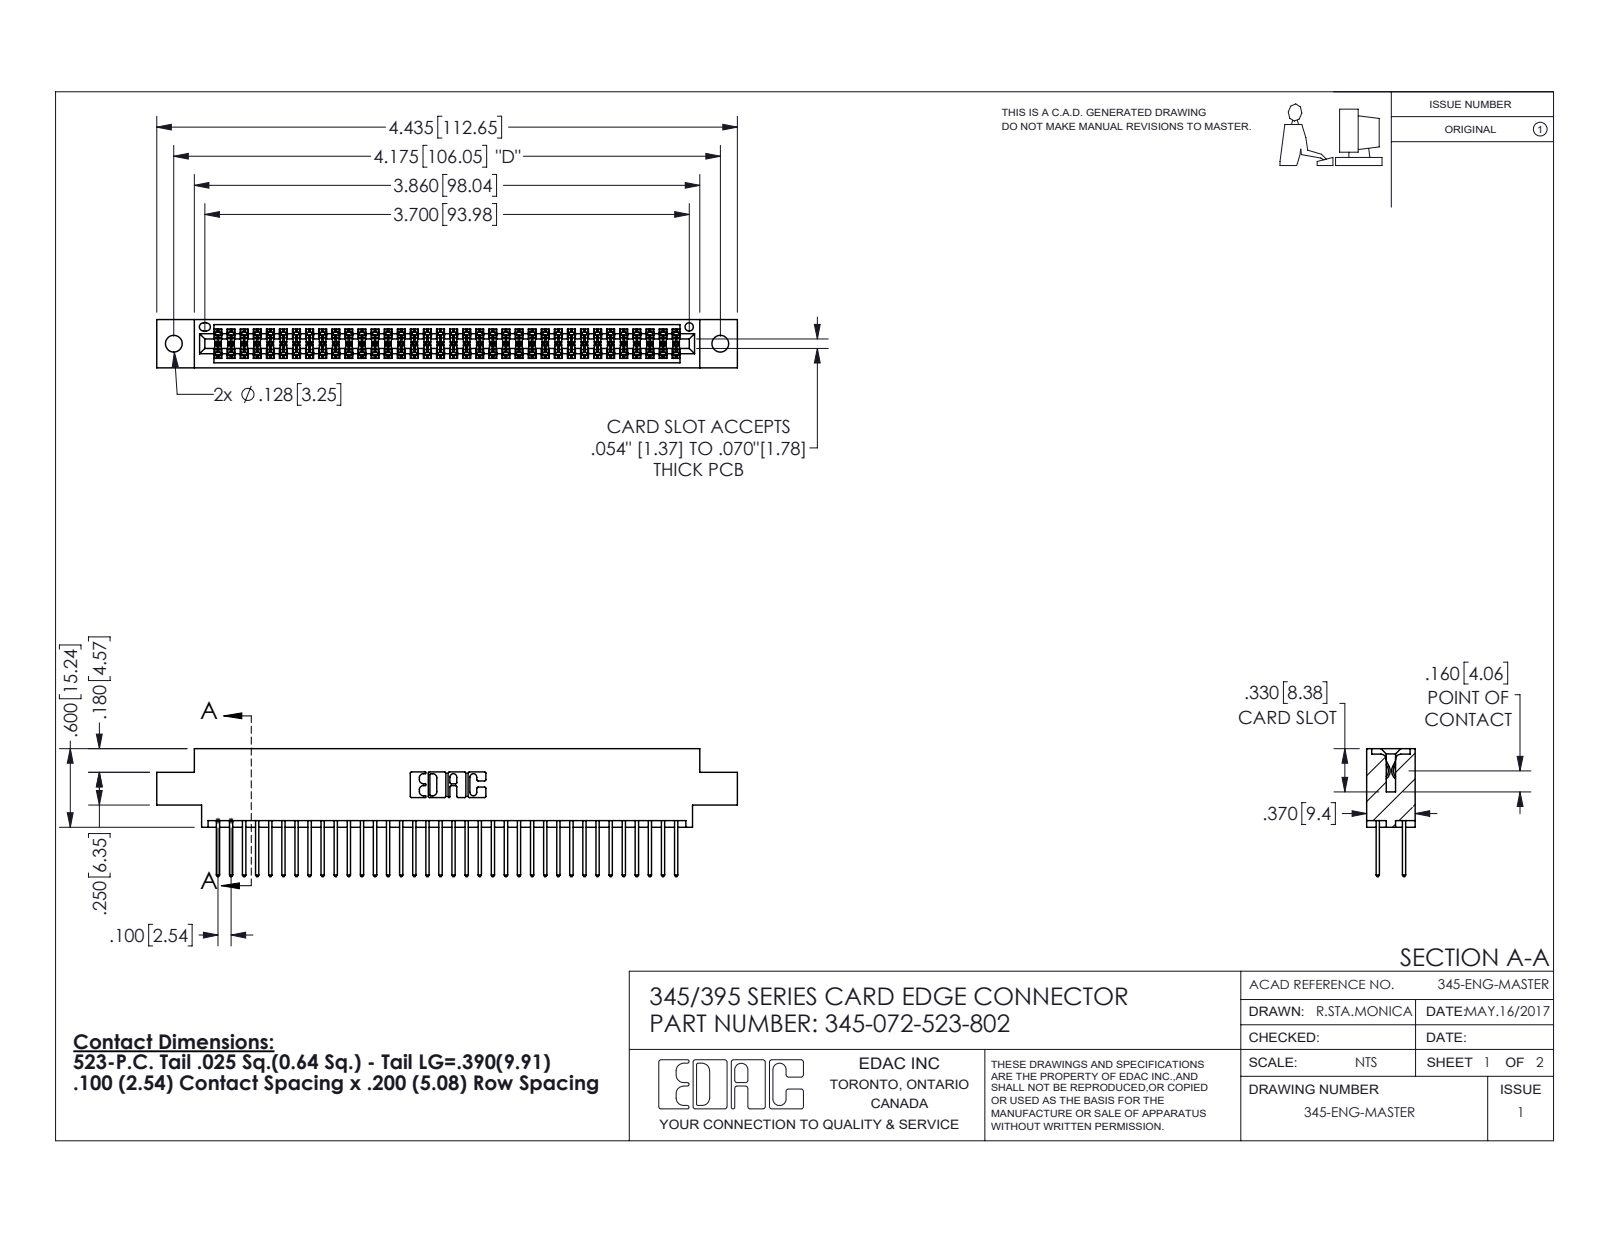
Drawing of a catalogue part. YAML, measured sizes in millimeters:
part_name: "345-292-001_345-293-123; 345 Part_0.170 Offset - 0.128 Dia; 345-072-523-802"
step_written_by: "SolidWorks 2016 (CONFIG_CONTROL_DESIGN)"
units: millimeters
bodies: {solids: 73, faces: 3730, planar: 2460, cylindrical: 1270, other: 0}
overall_size: [112.6, 24.8, 9.4]
volume: 10900
surface_area: 16500
round_holes:
  - {diameter: 3.3, count: 2}
  - {diameter: 1.6, count: 1}
partial_cylinders:
  - {radius: 0.2, count: 108}
  - {radius: 0.3, count: 72}
  - {radius: 0.3, count: 22}
  - {radius: 0.2, count: 6}
  - {radius: 0.8, count: 6}
  - {radius: 0.7, count: 3}
  - {radius: 0.4, count: 2}
  - {radius: 0.5, count: 2}
face_to_face_distances: [7.6, 1.8, 5.1, 2.5, 6.9, 0.6, 9.4, 5.7, 4.4, 3.8]
hole_center_spacings: [6.9, 100.1, 106]
